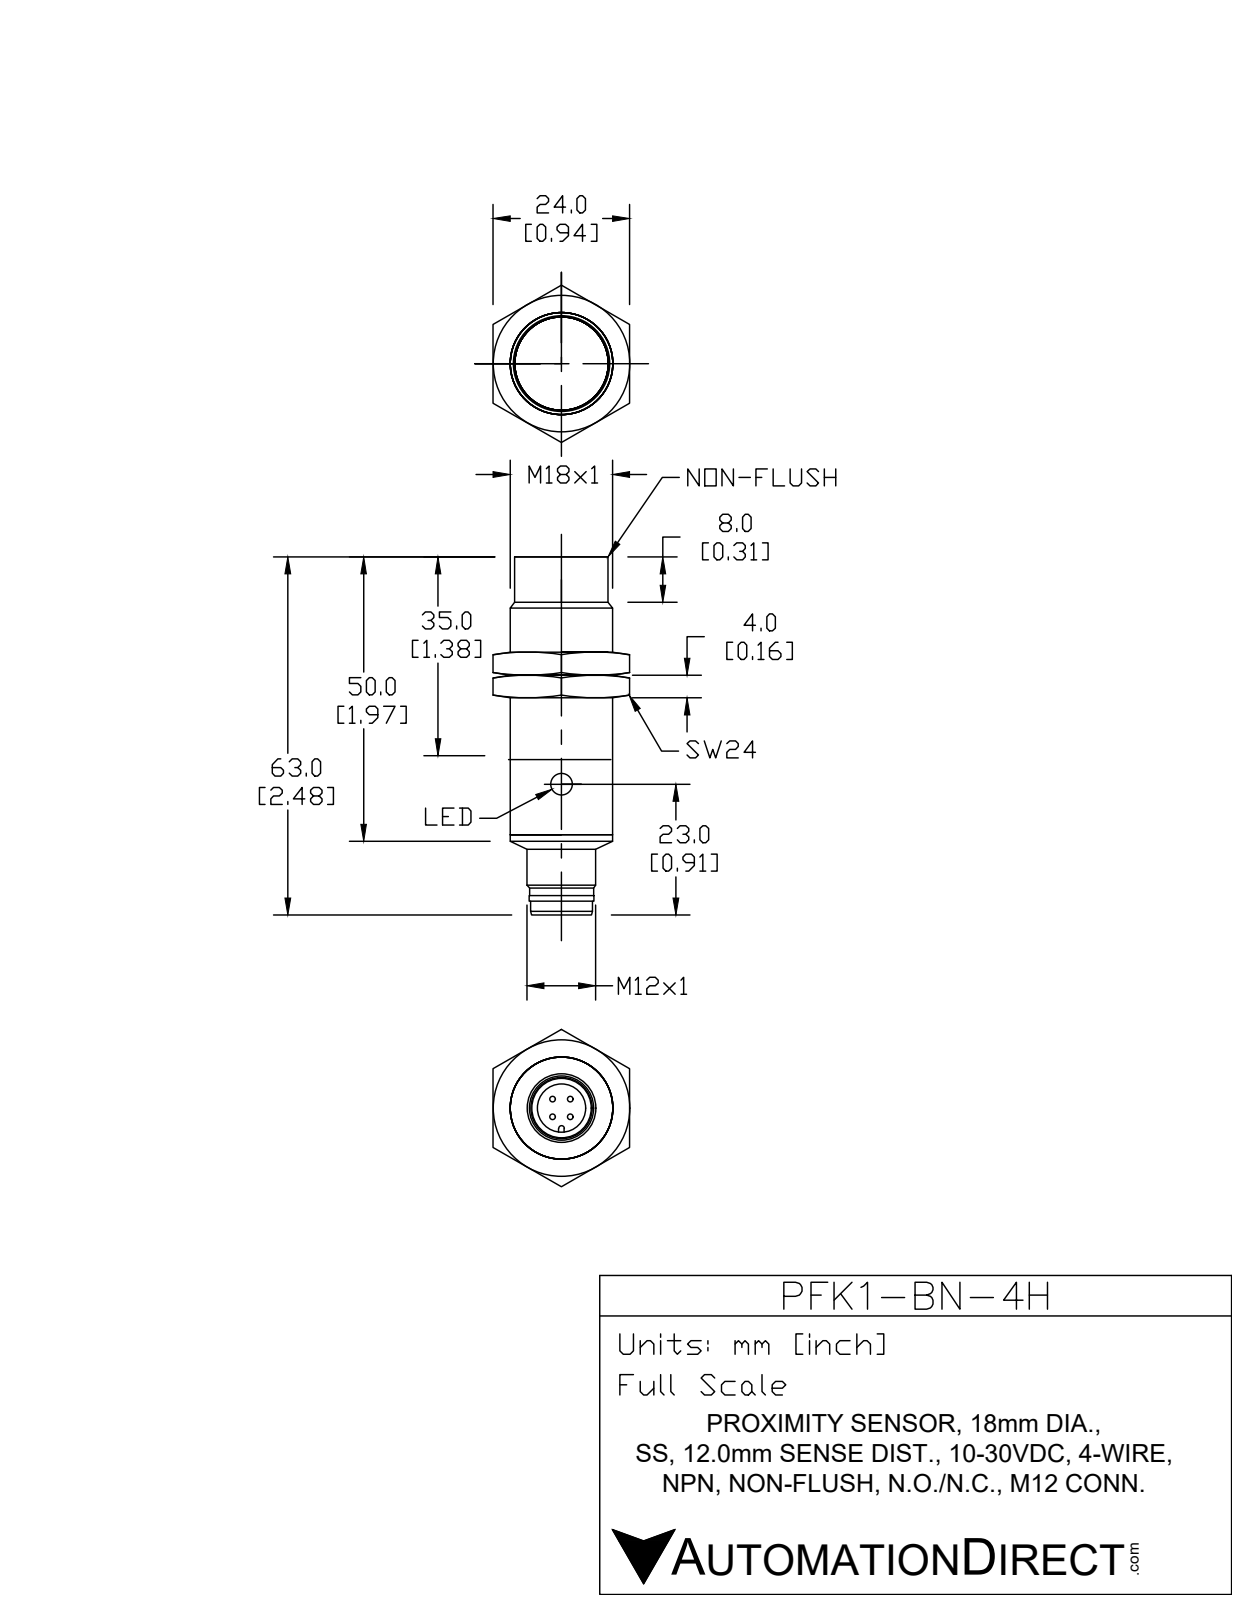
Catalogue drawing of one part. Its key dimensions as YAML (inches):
part_name: "PFK1-BN-4H"
step_written_by: "SolidWorks 2017 (AUTOMOTIVE_DESIGN)"
units: inches
bodies: {solids: 4, faces: 69, planar: 12, cylindrical: 35, other: 22}
overall_size: [2.484, 0.709, 0.709]
volume: 0.811
surface_area: 8.999
round_holes:
  - {diameter: 0.157, count: 1}
  - {diameter: 0.331, count: 1}
  - {diameter: 0.335, count: 1}
  - {diameter: 0.374, count: 1}
  - {diameter: 0.622, count: 1}
round_bosses_or_shafts:
  - {diameter: 0.039, count: 4}
  - {diameter: 0.709, count: 1}
  - {diameter: 0.472, count: 1}
  - {diameter: 0.413, count: 1}
  - {diameter: 0.37, count: 1}
partial_cylinders:
  - {radius: 0.024, count: 1}
  - {radius: 0.326, count: 1}
face_to_face_distances: [1.539, 0.394, 1.933, 2.087, 1.693, 0.154, 2.134, 1.74, 0.201, 0.047]
